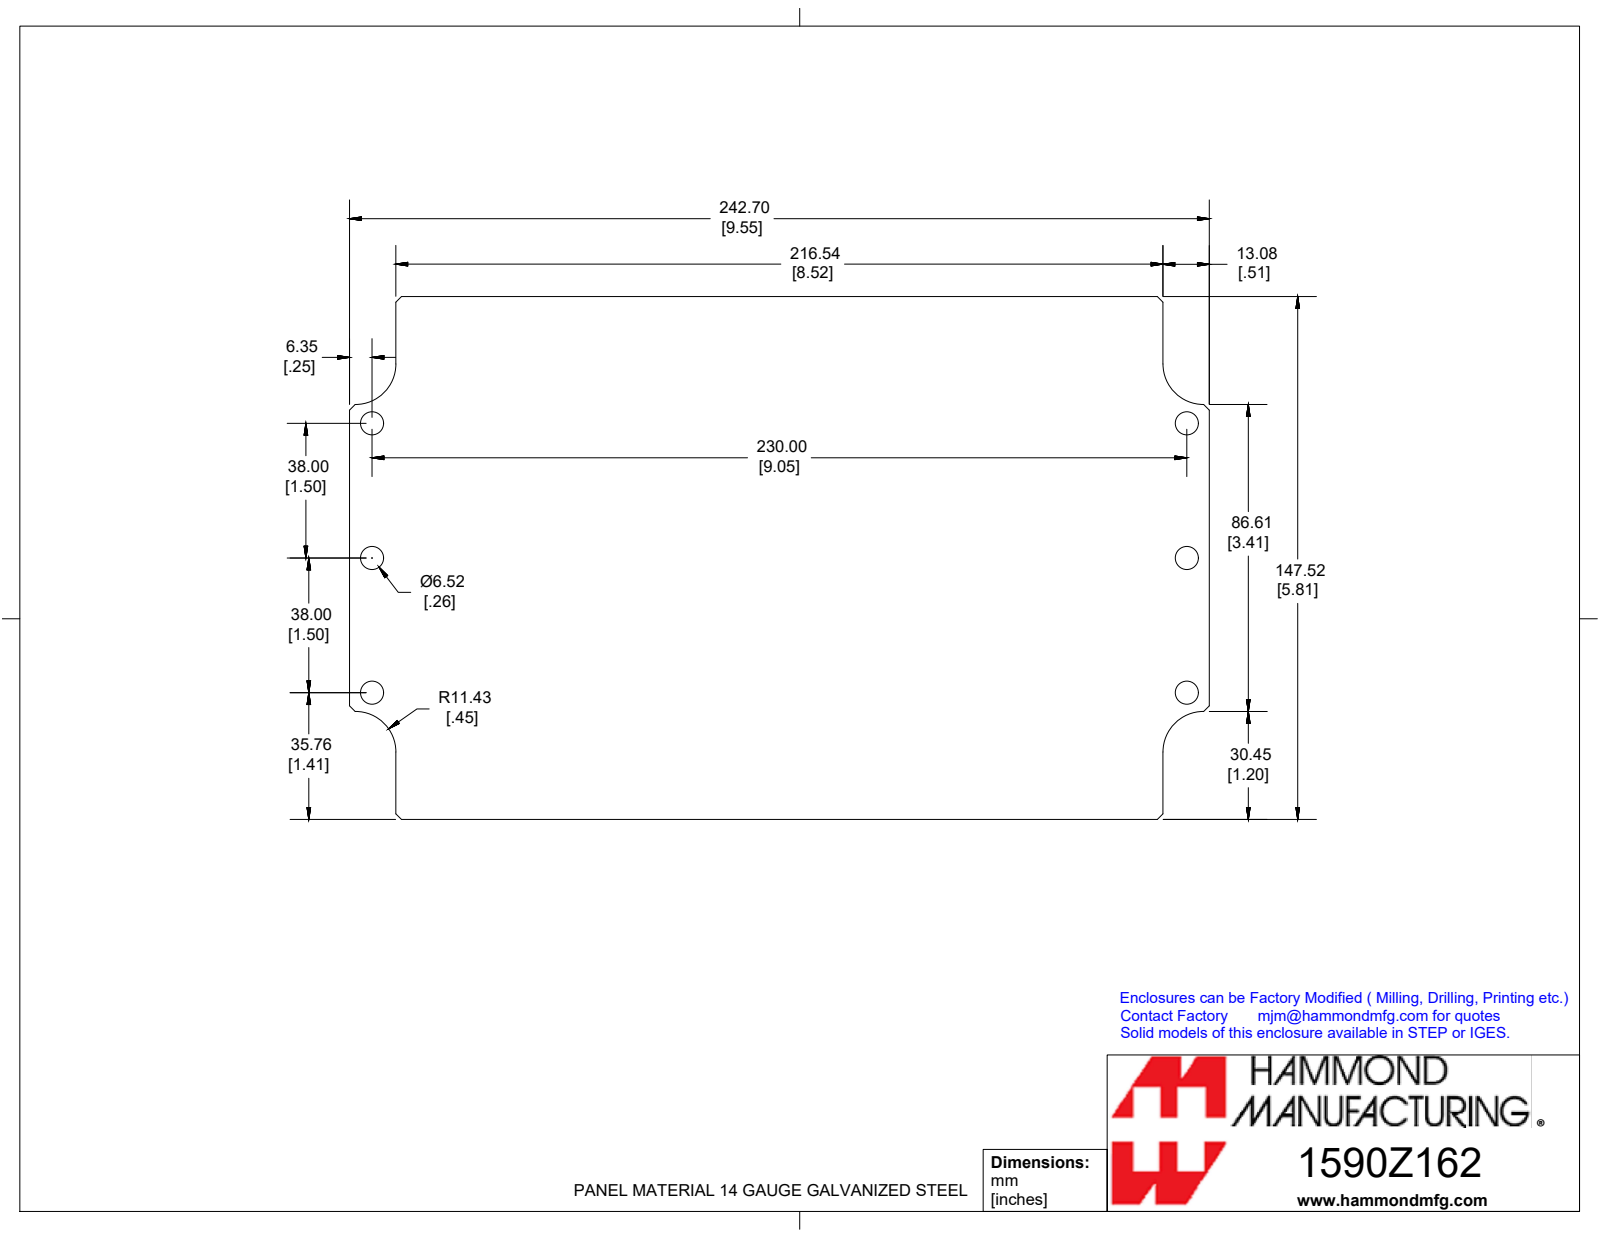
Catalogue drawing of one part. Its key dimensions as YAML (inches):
part_name: "1590Z162PL"
step_written_by: "SolidWorks 2019 (CONFIG_CONTROL_DESIGN)"
units: inches
bodies: {solids: 1, faces: 32, planar: 22, cylindrical: 10, other: 0}
overall_size: [9.555, 5.808, 0.064]
volume: 3.357
surface_area: 107.9
round_holes:
  - {diameter: 0.257, count: 6}
partial_cylinders:
  - {radius: 0.45, count: 4}
face_to_face_distances: [0.063, 5.808, 9.555, 0.515, 9.04, 8.525, 0.483, 9.561, 10.045, 9.078]
hole_center_spacings: [1.496, 9.178, 9.055, 2.992, 9.537]
